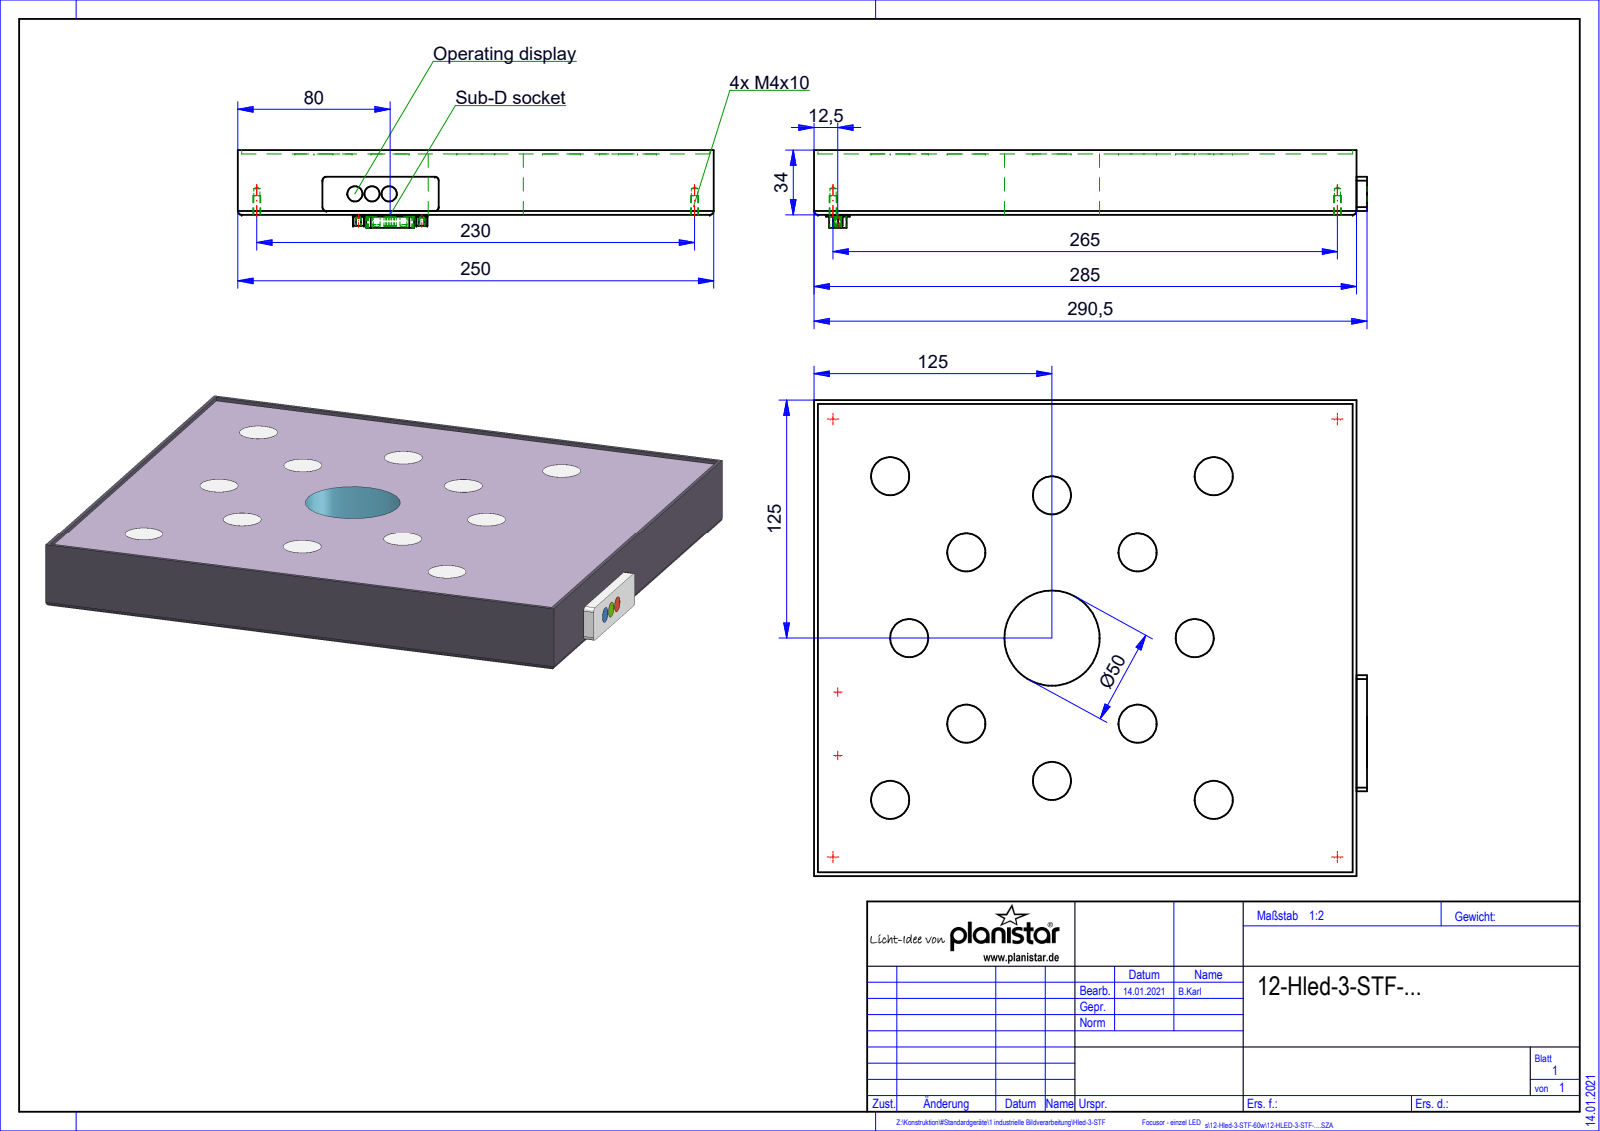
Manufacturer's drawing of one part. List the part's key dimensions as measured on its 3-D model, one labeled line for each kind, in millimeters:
Part name (STEP PRODUCT): Root; Baugruppe_Xled-2-VD; QUADER_0; Baugruppe_Baugruppe (+5 more)
STEP written by: HiCAD 2015 2002.1 Build 408 (AUTOMOTIVE_DESIGN)
Units: millimetres
Bodies: 12 solids, 164 faces (84 planar, 67 cylindrical, 13 other)
Overall size (bounding box): 290.55 × 250 × 40.8
Volume: 2 227 000 mm³ · Surface area: 187 278 mm²
Round holes (diameter × count): ⌀20 ×12, ⌀3.3 ×4, ⌀4 ×4, ⌀2.5 ×2, ⌀3 ×2, ⌀50 ×1
Round bosses / shafts (diameter × count): ⌀1 ×5, ⌀8 ×3, ⌀3.6 ×2
Partial cylindrical surfaces — rounded edges, fillets, slot ends (radius × count): R0.2 ×12, R2 ×8, R1.5 ×4, R2.1 ×4, R2.5 ×4
Main face-to-face distances: 32, 250, 285, 2, 31.95, 34, 2.05, 248, 283, 290.5
Hole centre spacings: 54.08, 85.59, 128.16, 136.01, 181.18, 56.57, 63.64, 75
